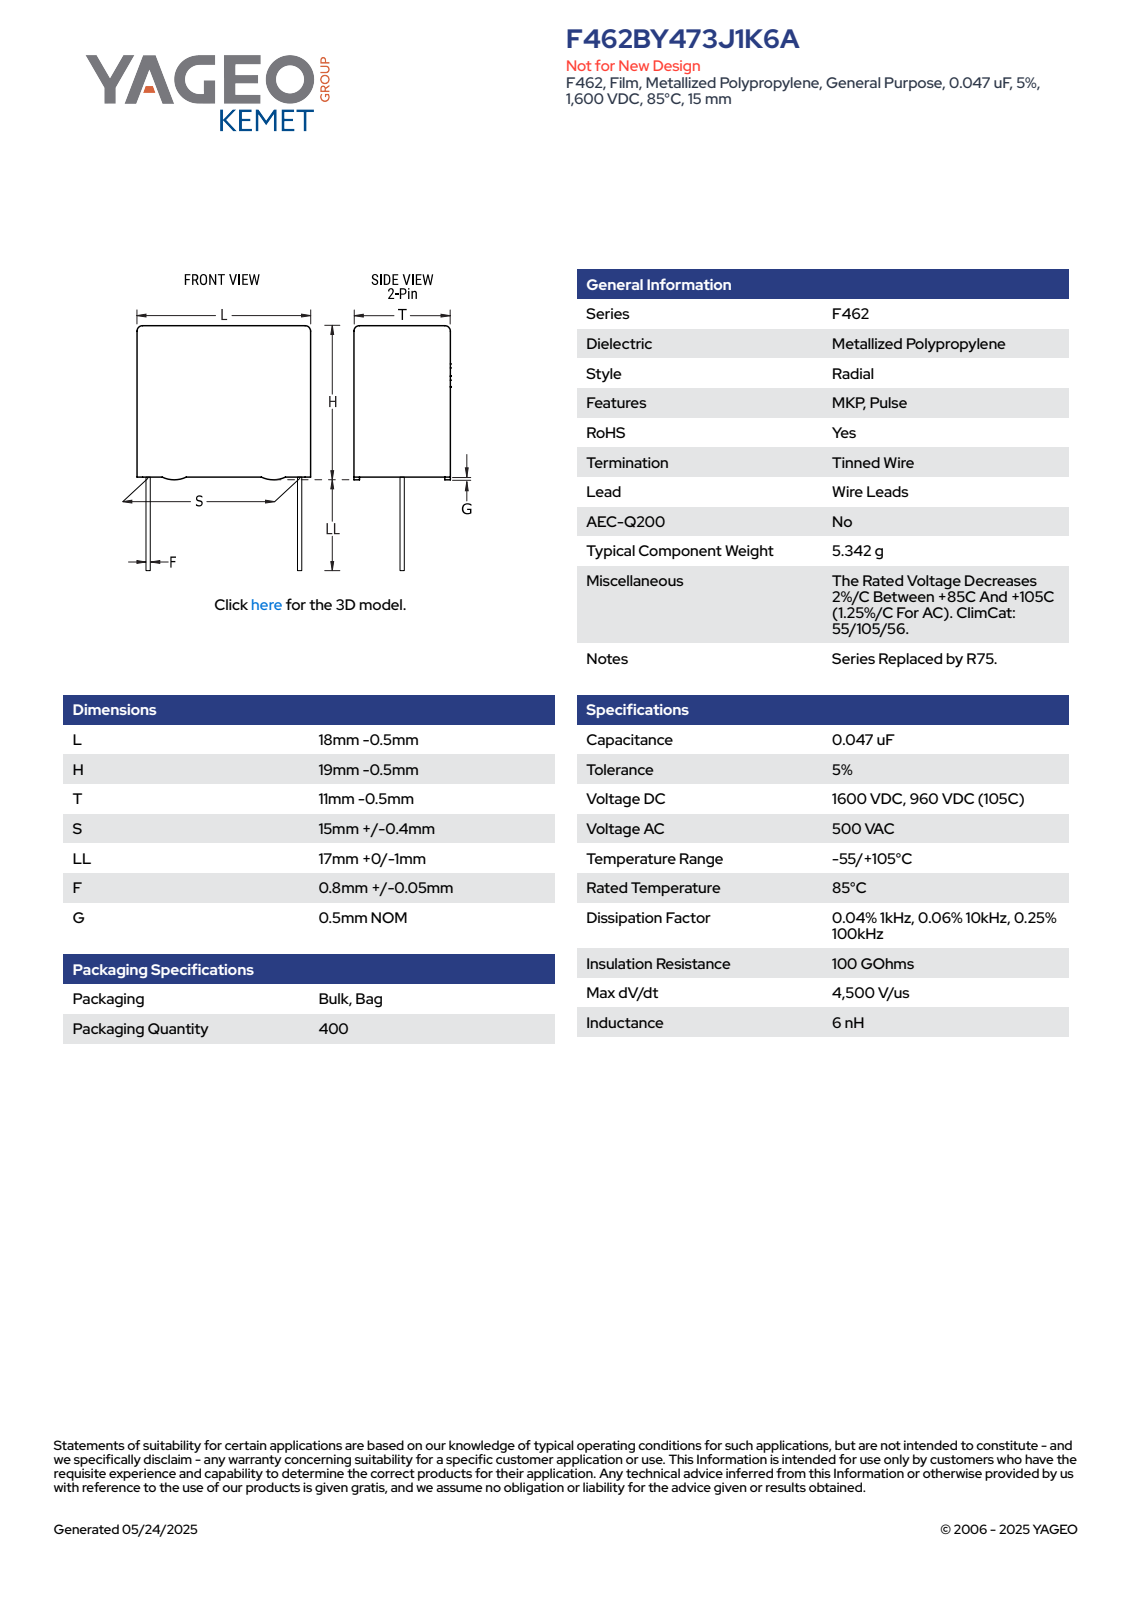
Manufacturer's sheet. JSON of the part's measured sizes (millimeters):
{"part_name": "CFR_RBG_18X19X11_L17.5H18.5T10.5S15LL17F0.85G0.5", "step_written_by": "SolidWorks 2014 (AUTOMOTIVE_DESIGN)", "units": "millimeters", "bodies": {"solids": 4, "faces": 89, "planar": 81, "cylindrical": 8, "other": 0}, "overall_size": [35.5, 17.5, 10.51], "volume_mm3": 3328, "surface_area_mm2": 1503, "round_bosses_or_shafts": [[0.85, 2]], "partial_cylinders_radius": [[0.5, 4]], "face_to_face_distances": [10.5, 17.5, 18, 10.51, 0.5, 18.5, 0.6, 9.9, 0.61, 9.3]}
